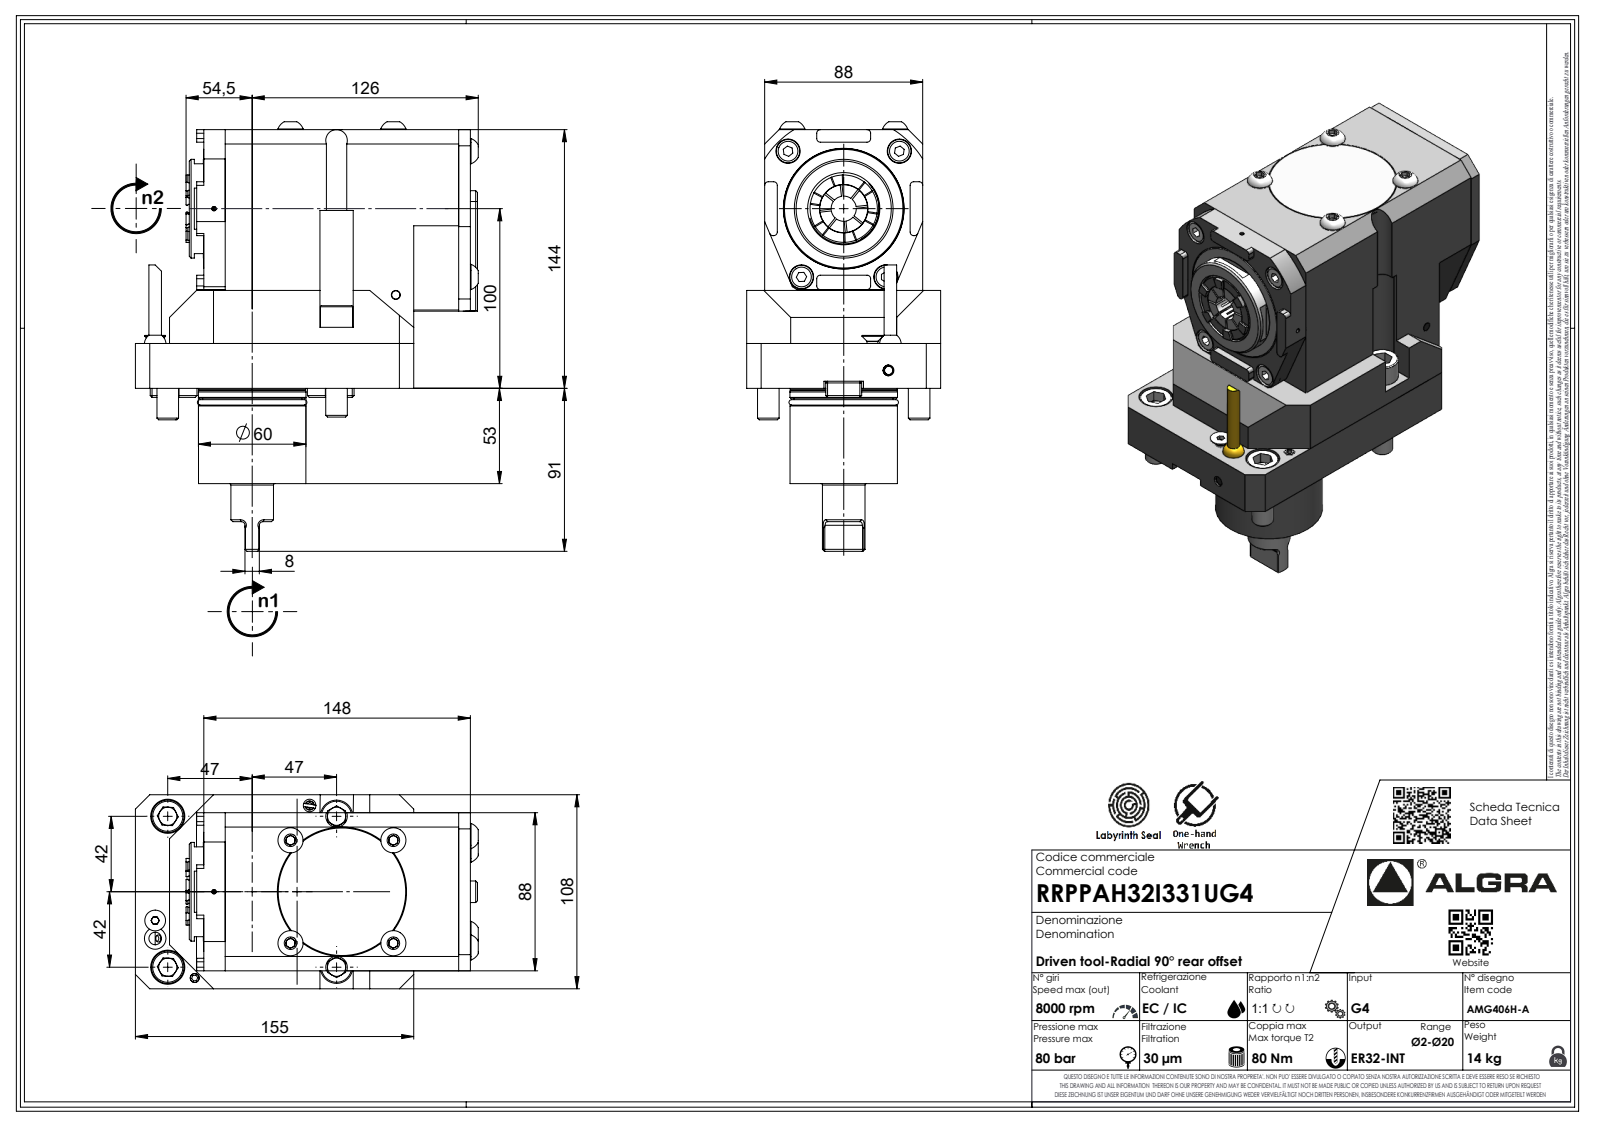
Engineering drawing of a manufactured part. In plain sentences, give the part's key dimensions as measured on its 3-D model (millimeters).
The part is named "RRPPAH32I331UG4". Its 3-D file was written by "SolidWorks 2023 (AUTOMOTIVE_DESIGN)". It is 1 solid with 600 faces: 387 planar, 83 cylindrical and 130 other. Overall it measures 239.1 by 190.9 by 108 millimeters. Its volume is 2 141 000 cubic millimeters and its surface area 133 093 square millimeters. Round holes: 2 of diameter 12, 1 of diameter 2.1, 1 of diameter 4. Round bosses or shafts: 8 of diameter 14, 2 of diameter 18, 2 of diameter 12, 1 of diameter 59.9, 1 of diameter 59.8, 1 of diameter 59.5, 1 of diameter 55.2, 1 of diameter 55. Partial cylindrical surfaces (rounded edges, fillets, slot ends): 19 of radius 2, 7 of radius 0.33, 7 of radius 0.52, 7 of radius 3.7, 4 of radius 3, 2 of radius 1, 2 of radius 9.25, 1 of radius 0.21. The main face-to-face distances are 98, 10, 144, 88, 108, 31.5, 30, 54.5, 89.5, 148.4. The hole center spacings are 84.
